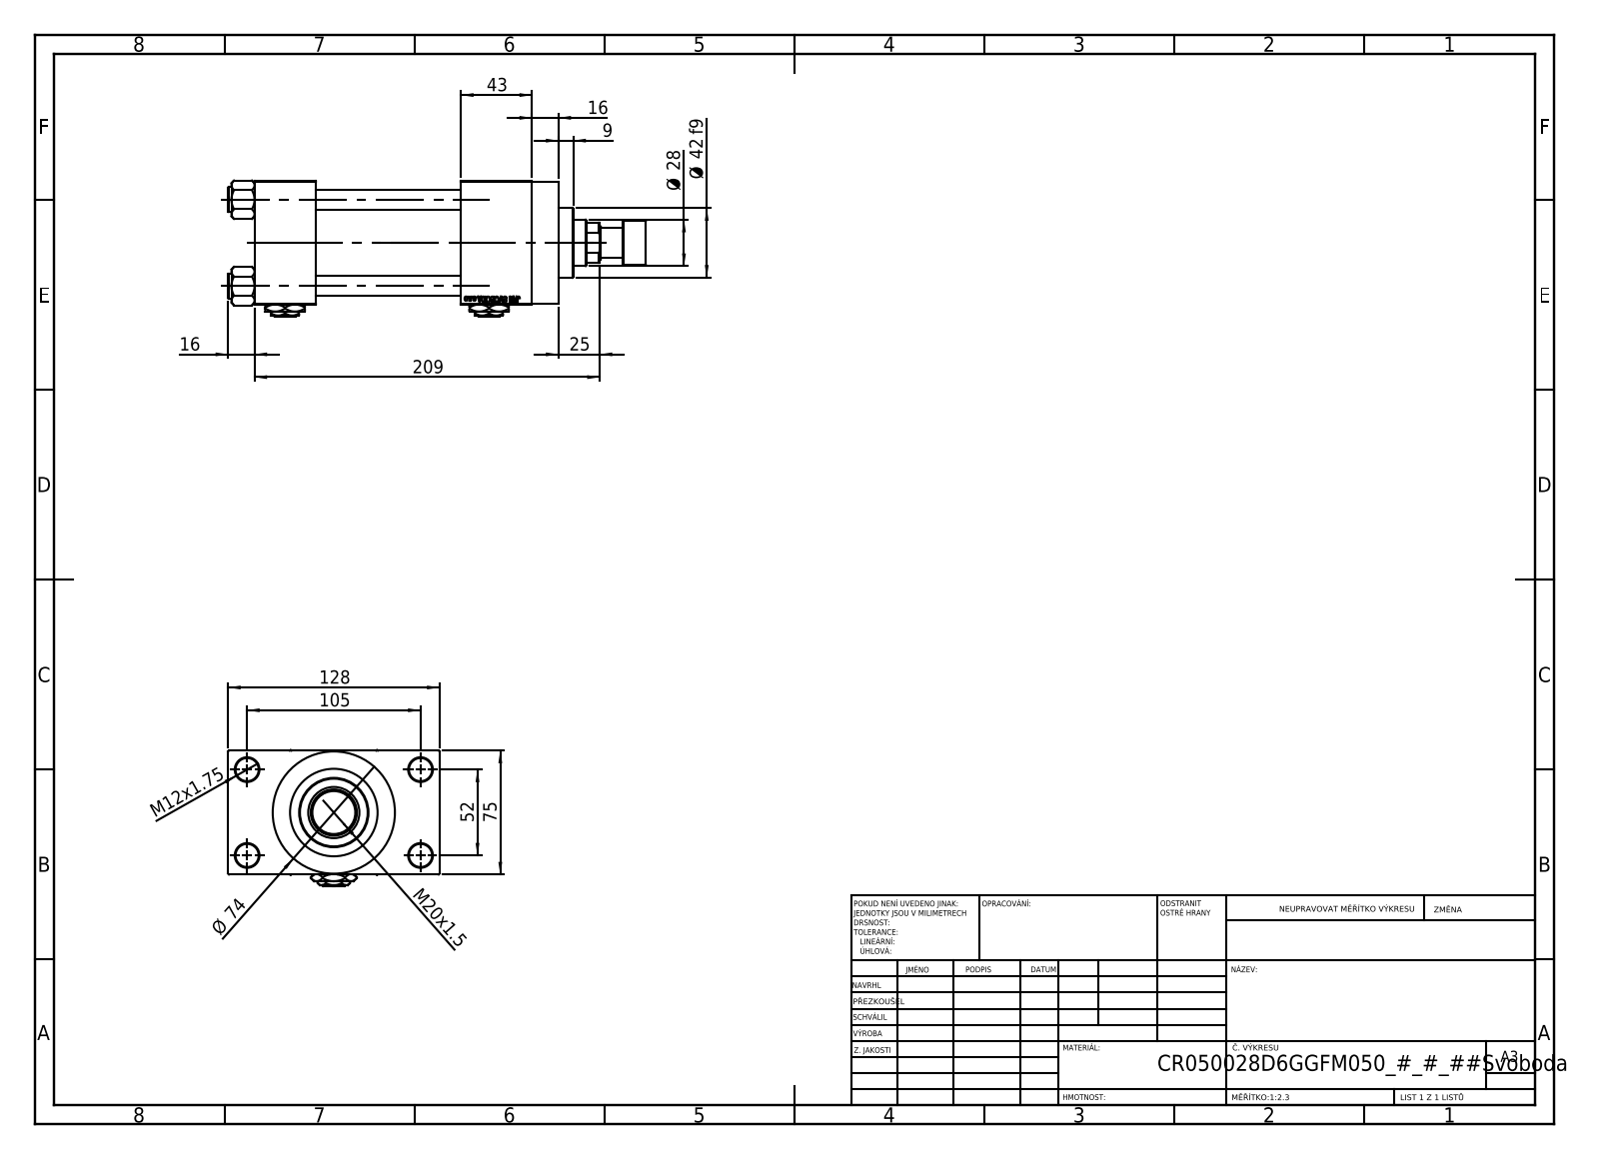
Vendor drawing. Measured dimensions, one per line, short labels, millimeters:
name: V215CR_D_Body; V215_VC_A; V215CR_D_TYCINKA; Zatka_pro_OIL_PORT (+3 more)
written by: SolidWorks 2019 (CONFIG_CONTROL_DESIGN)
unit: mm
bodies: 14 solids, 1219 faces (549 planar, 104 cylindrical, 566 other)
size: 253 × 128 × 82.27
volume: 869 505 mm³; area: 193 514 mm²
holes: 4× ⌀12, 4× ⌀14, 2× ⌀7, 2× ⌀20.96, 2× ⌀30, 1× ⌀18.5, 1× ⌀28, 1× ⌀31, 1× ⌀41, 1× ⌀50, 1× ⌀53
bosses: 4× ⌀15, 1× ⌀74, 1× ⌀56, 1× ⌀42, 1× ⌀27, 1× ⌀18
face distances: 75, 88, 37, 125, 26.5, 101.5, 168, 131, 43, 16
hole spacings: 26.35, 36.98, 52.3, 58.43, 58.59, 78.65, 94.37, 52
